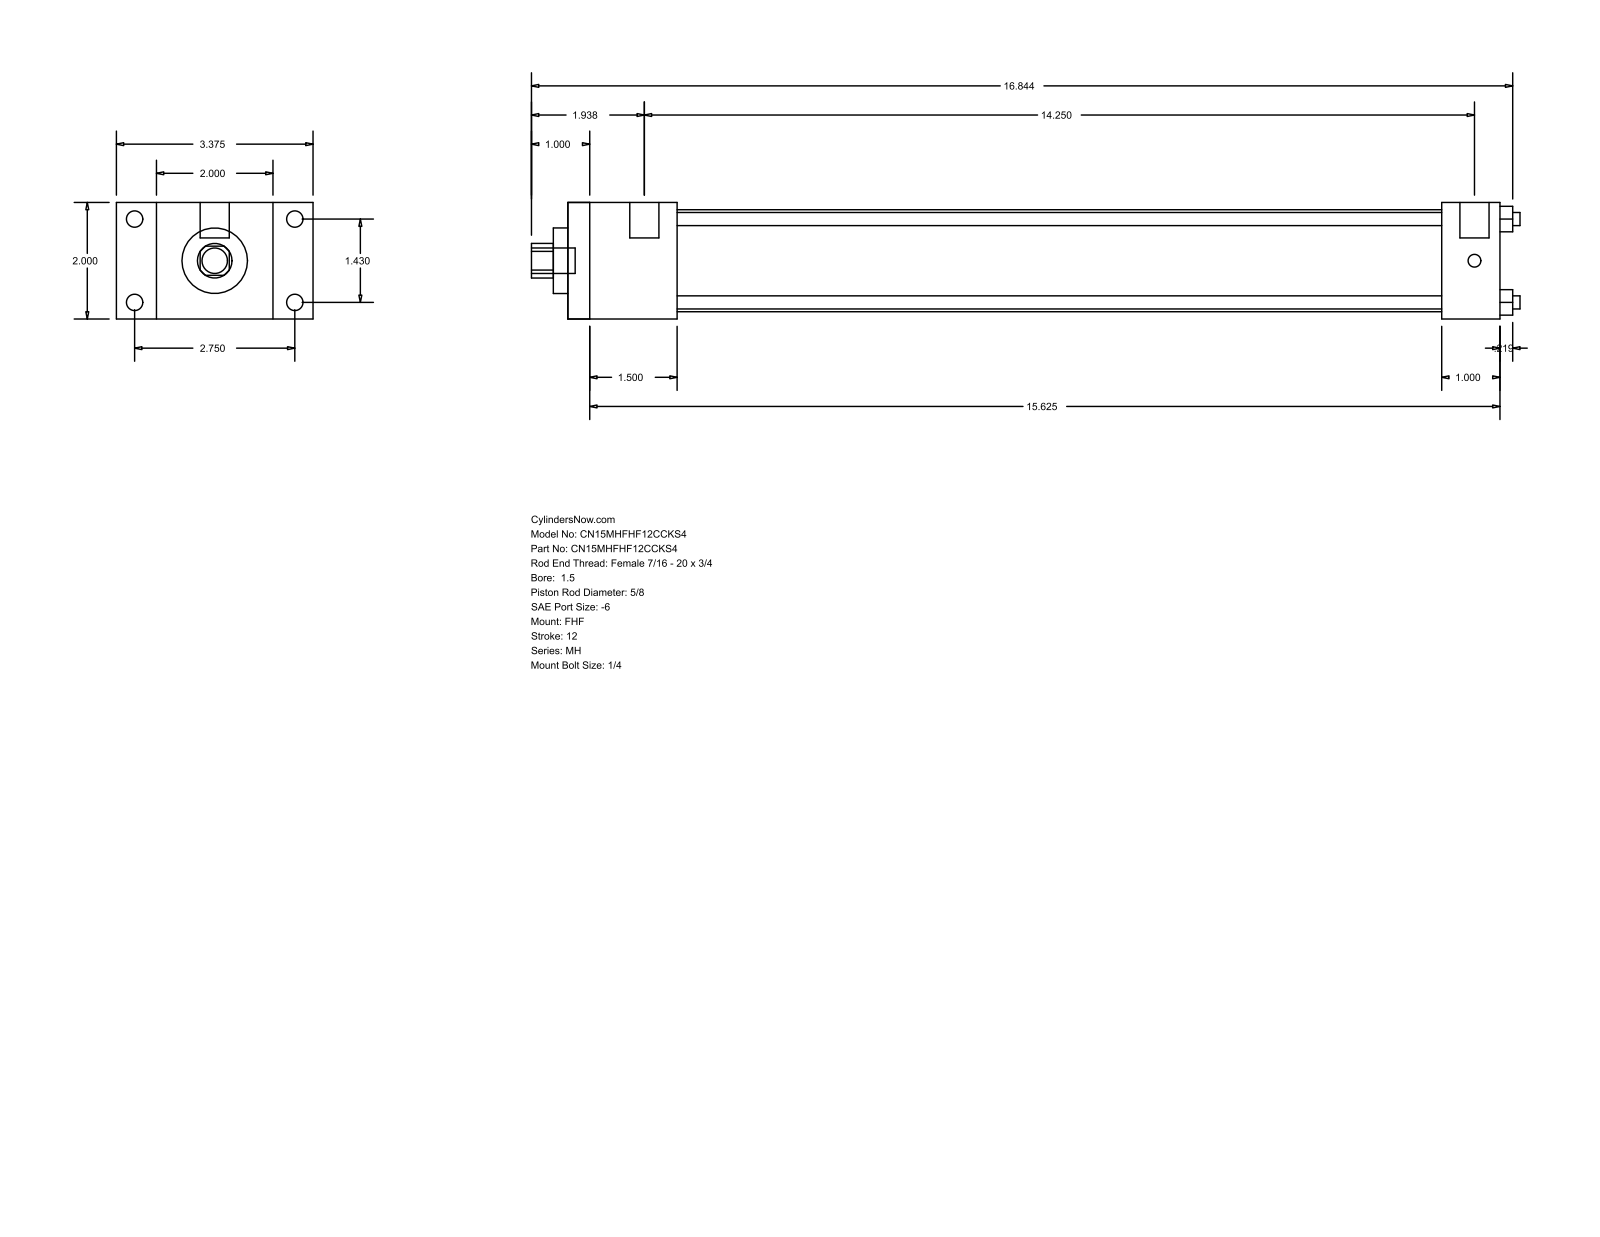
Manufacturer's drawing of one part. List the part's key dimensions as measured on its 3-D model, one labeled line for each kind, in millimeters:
Part name (STEP PRODUCT): MH_FHF__0150_0.625
STEP written by: GSSL Pune (CONFIG_CONTROL_DESIGN)
Units: millimetres
Bodies: 0 solids, 88 faces (60 planar, 28 cylindrical, 0 other)
Overall size (bounding box): 431.01 × 85.72 × 50.8
Round holes (diameter × count): ⌀5.71 ×4, ⌀15.88 ×1, ⌀28.57 ×1, ⌀44.45 ×1
Round bosses / shafts (diameter × count): ⌀7.14 ×4, ⌀5.56 ×4, ⌀12.7 ×2, ⌀11.11 ×1
Partial cylindrical surfaces — rounded edges, fillets, slot ends (radius × count): R7.54 ×1
Main face-to-face distances: 50.8, 17.46, 68.26, 47.62, 85.72, 406.39, 358.77, 381, 333.38, 25.39
Hole centre spacings: 25.68, 36.32, 51.36
